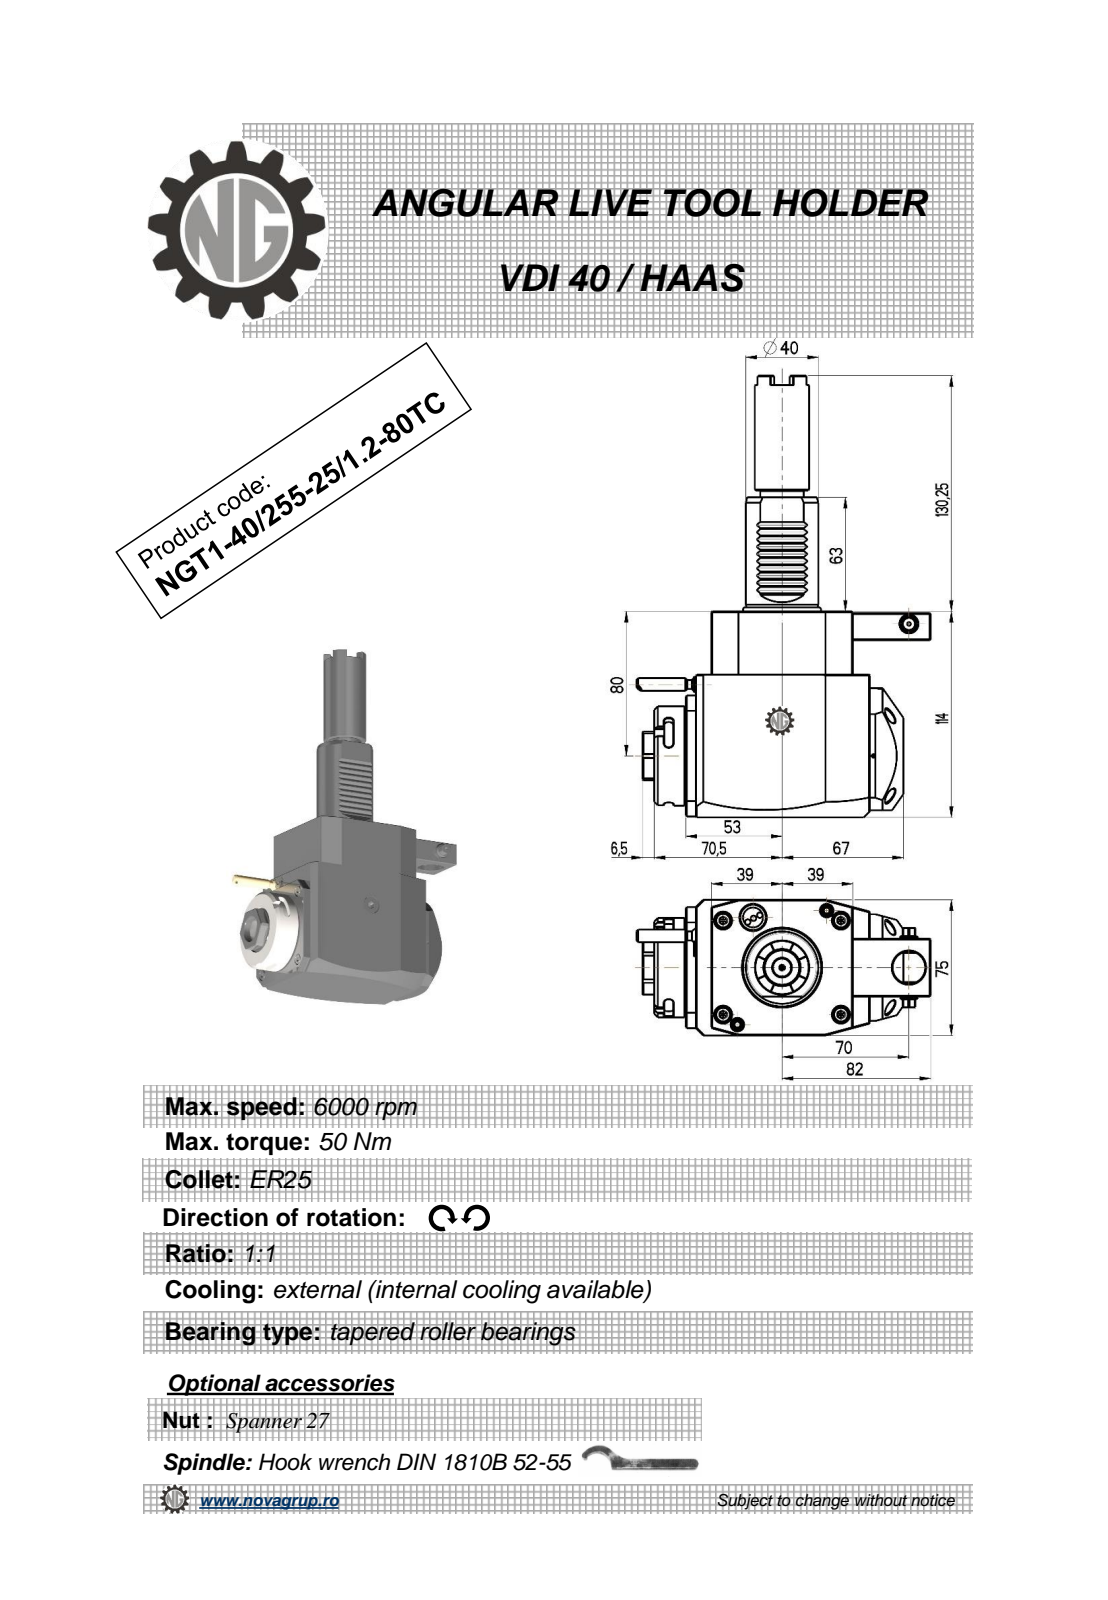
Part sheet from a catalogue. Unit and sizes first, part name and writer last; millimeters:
Units: millimetres
Overall size (bounding box): 244.25 × 162.33 × 75
Round holes (diameter × count): ⌀18 ×2, ⌀2 ×1, ⌀2.5 ×1, ⌀3 ×1, ⌀9.5 ×1, ⌀20 ×1
Round bosses / shafts (diameter × count): ⌀8.96 ×2, ⌀55 ×1, ⌀48 ×1, ⌀40 ×1, ⌀30 ×1, ⌀24 ×1, ⌀10 ×1, ⌀7 ×1
Partial cylindrical surfaces — rounded edges, fillets, slot ends (radius × count): R0.3 ×10, R2.5 ×6, R180 ×2, R0.5 ×1, R3.85 ×1, R4.25 ×1, R15 ×1, R24.5 ×1
Main face-to-face distances: 75, 114, 14, 17.5, 109.5, 79, 92, 78, 31.5, 98
Hole centre spacings: 37.35, 43.2, 70, 72.5
Volume: 1 003 000 mm³ · Surface area: 79 849 mm²
Bodies: 1 solid, 387 faces (213 planar, 86 cylindrical, 88 other)
Part name (STEP PRODUCT): NGT1_40_255_25_1_2_80TC
STEP written by: PRO/ENGINEER BY PARAMETRIC TECHNOLOGY CORPORATION, 2010280 (CONFIG_CONTROL_DESIGN)
